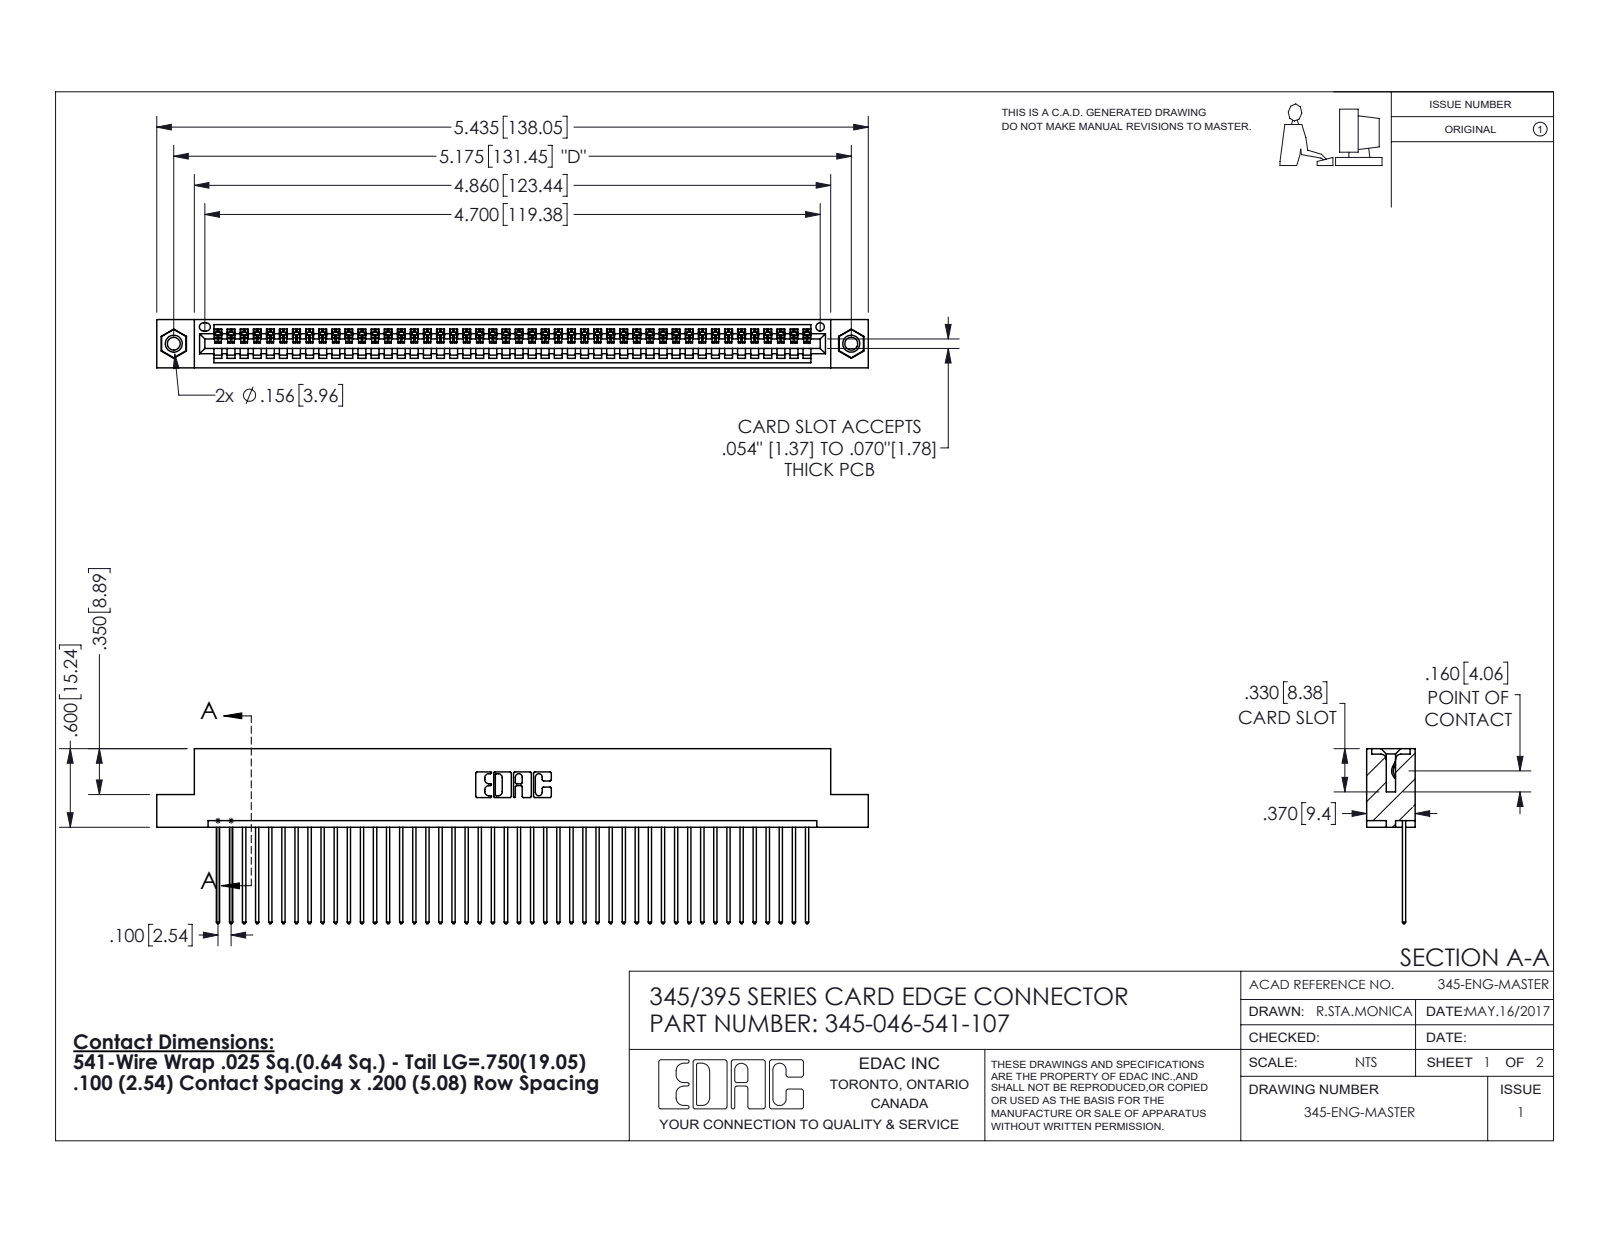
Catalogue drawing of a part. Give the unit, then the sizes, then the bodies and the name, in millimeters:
Units: millimetres
Overall size (bounding box): 138 × 34 × 9.4
Round holes (diameter × count): ⌀2.5 ×2, ⌀3.2 ×2, ⌀4 ×2, ⌀1.6 ×1
Round bosses / shafts (diameter × count): ⌀3.9 ×2
Partial cylindrical surfaces — rounded edges, fillets, slot ends (radius × count): R0.2 ×92, R0.3 ×92, R0.3 ×22, R0.2 ×6, R0.8 ×6, R0.7 ×3, R0.8 ×2, R1 ×2
Main face-to-face distances: 1.8, 7.6, 2.5, 6.9, 0.6, 9.4, 5.1, 5.7, 3.8, 1.8
Hole centre spacings: 6.9, 125.5, 131.4
Volume: 13 300 mm³ · Surface area: 18 630 mm²
Bodies: 49 solids, 2854 faces (1952 planar, 886 cylindrical, 16 other)
Part name (STEP PRODUCT): 345-046-541-107; 345-292-001_345-293-141; 345 Part_Flush Mounting Lugs - 0.156 Dia-TI; 345-250-001_345-250-005-103
STEP written by: SolidWorks 2016 (CONFIG_CONTROL_DESIGN)
